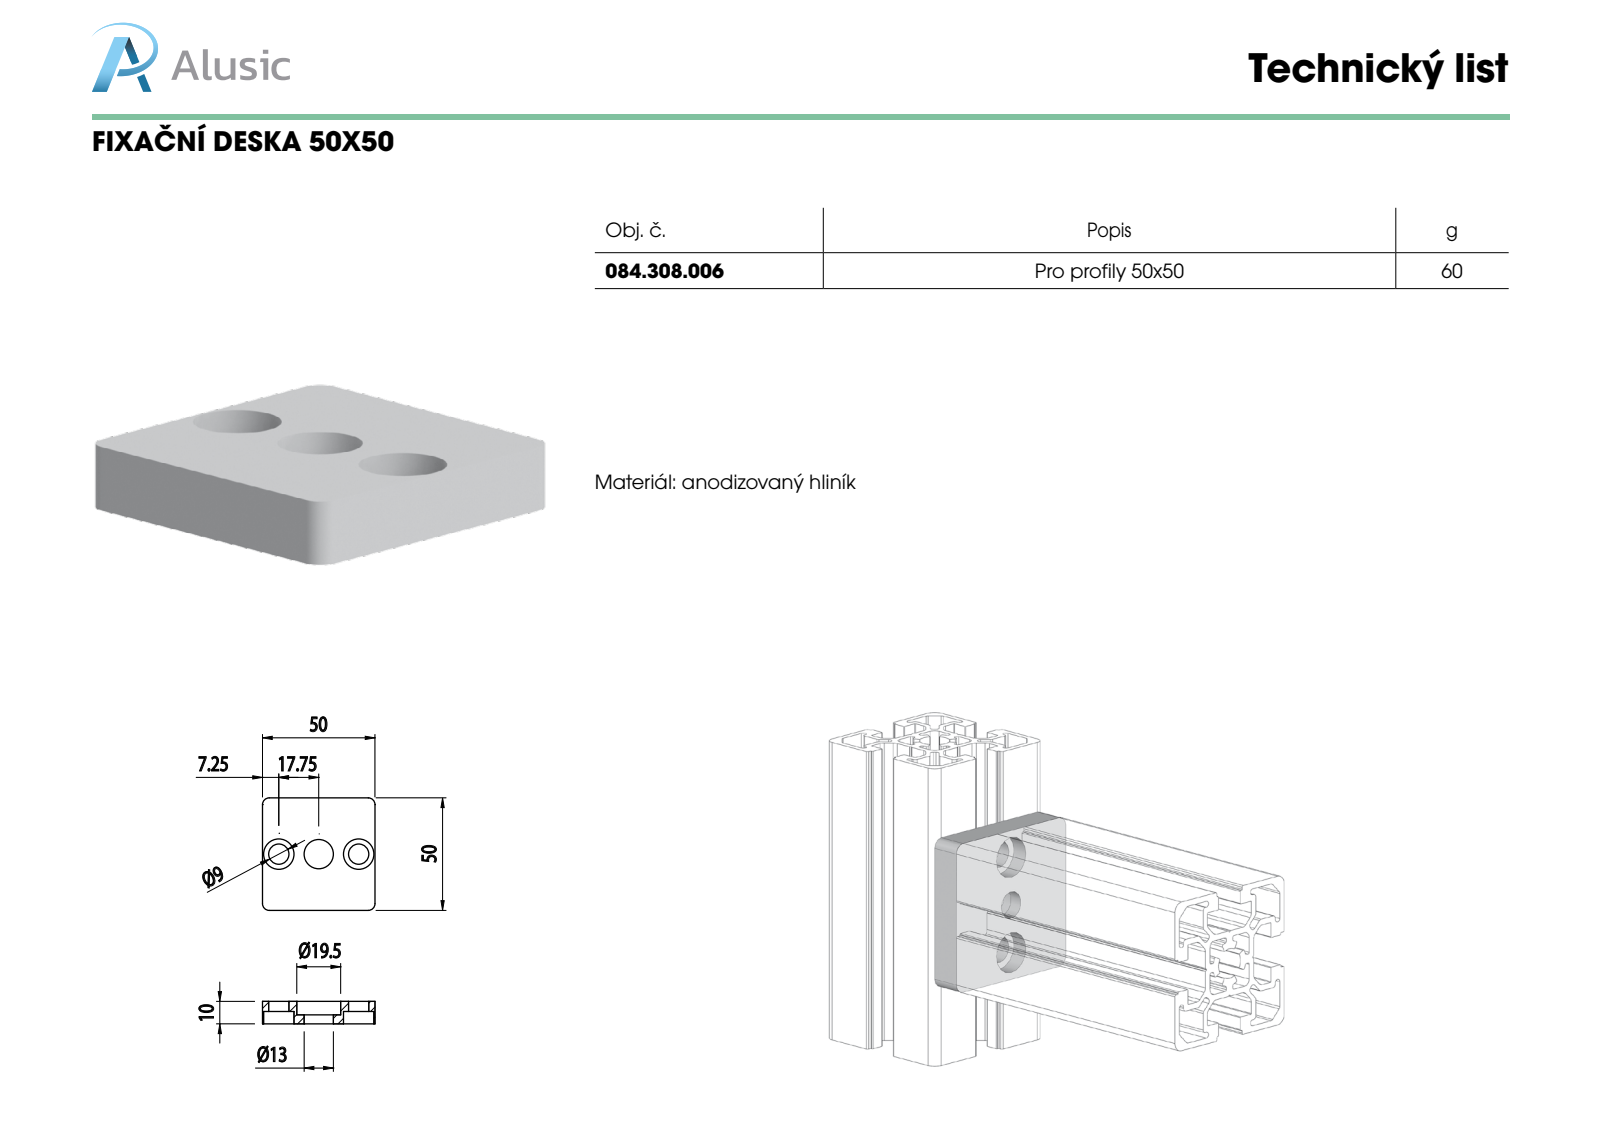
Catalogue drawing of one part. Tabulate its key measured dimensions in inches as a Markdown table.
| quantity | value |
| --- | --- |
| part name | 084.308.006 |
| STEP written by | SolidWorks 2012 (CONFIG_CONTROL_DESIGN) |
| units | inches |
| bodies | 1 solid, 25 faces (9 planar, 16 cylindrical, 0 other) |
| overall size | 1.969 × 1.969 × 0.394 |
| volume | 1.248 in³ |
| surface area | 11.88 in² |
| round holes (diameter × count) | 0.354 × 2, 0.531 × 2, 0.512 × 1, 0.768 × 1 |
| partial cylindrical surfaces (radius × count) | 0.118 × 4 |
| main face-to-face distances | 0.394, 1.969, 0.236, 0.157, 0.177, 0.059, 0.217 |
| hole center spacings | 0.699, 1.398 |
